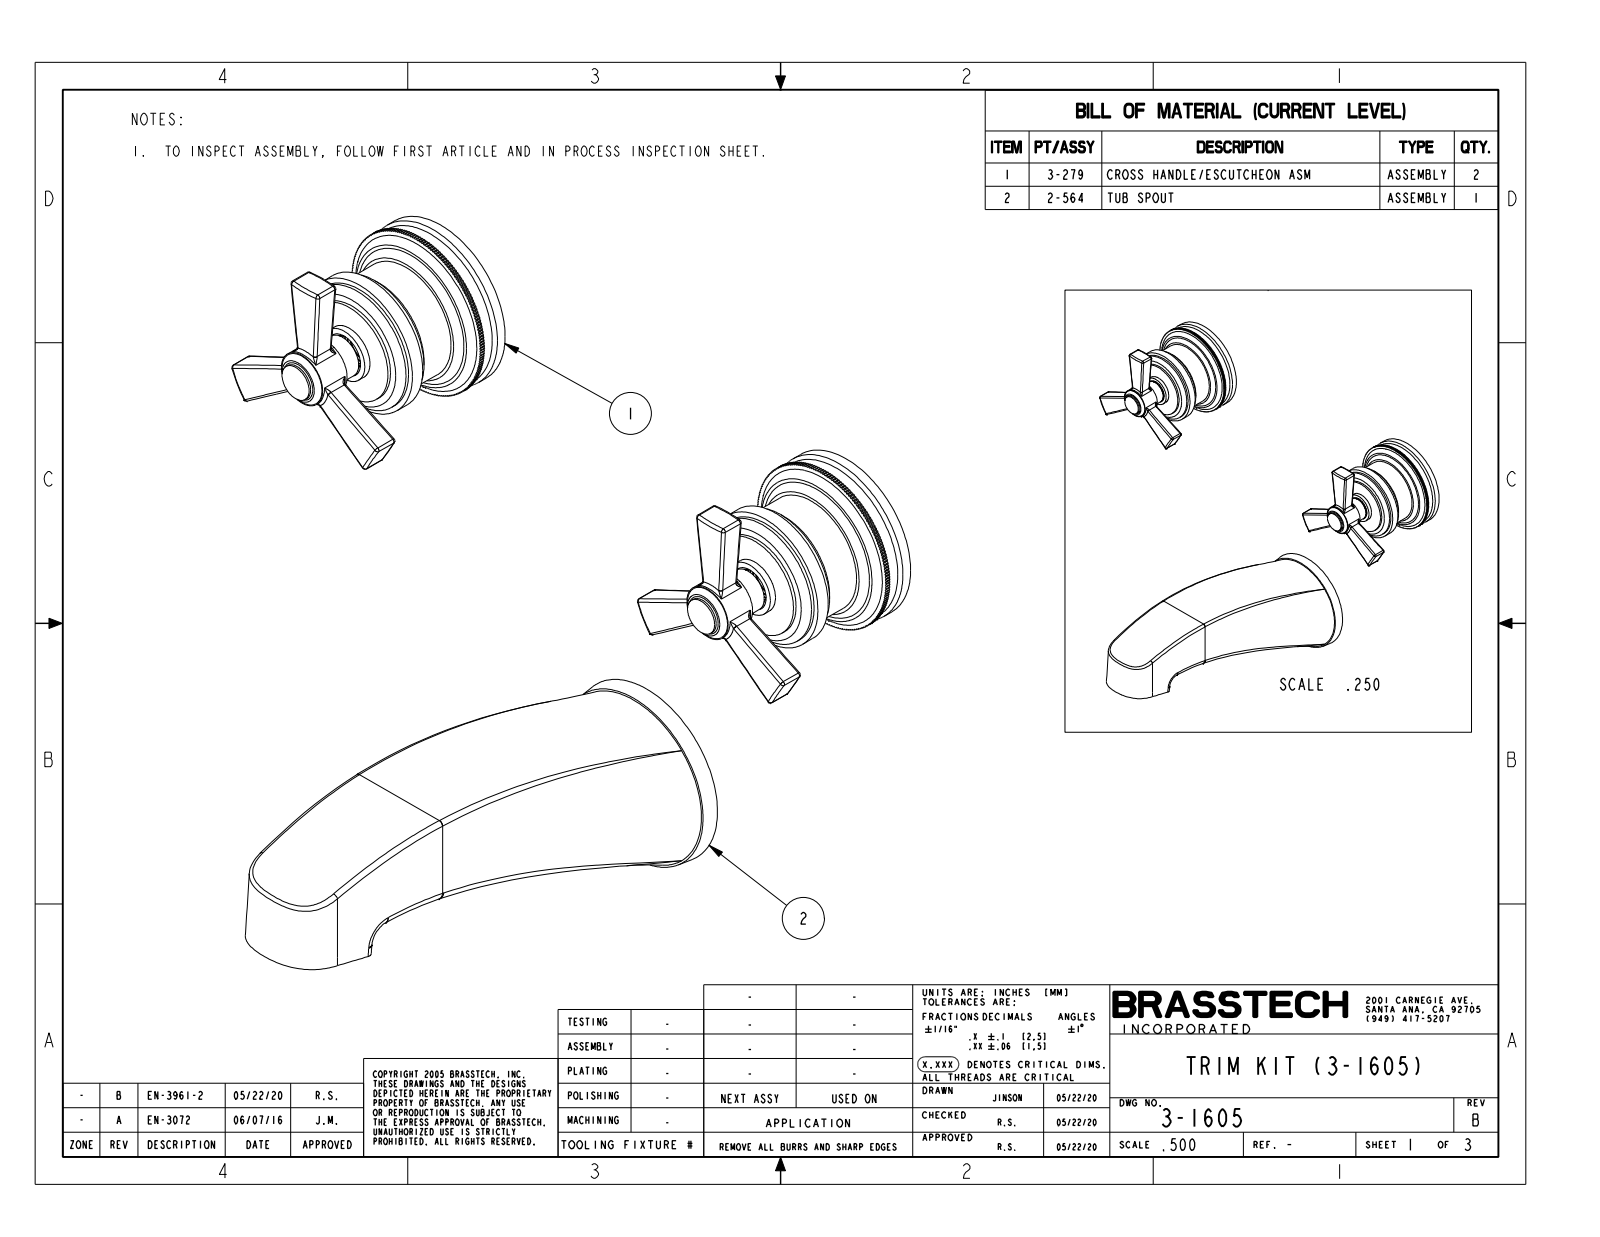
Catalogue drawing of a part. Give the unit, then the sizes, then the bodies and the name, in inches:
Units: inches
Overall size (bounding box): 10.714 × 8.875 × 7.429
Round bosses / shafts (diameter × count): ⌀2.5 ×2, ⌀2.4 ×2, ⌀2.05 ×2, ⌀1.9 ×2, ⌀1.75 ×2, ⌀1.5 ×2, ⌀0.8 ×2, ⌀0.625 ×2
Partial cylindrical surfaces — rounded edges, fillets, slot ends (radius × count): R0.04 ×12, R0.1 ×12
Main face-to-face distances: 0.062, 1.837, 1.775, 0.2, 0.1, 1.3, 0.15, 0.4, 1.375, 0.9
Volume: 36.29 in³ · Surface area: 117.7 in²
Bodies: 3 solids, 1419 faces (772 planar, 432 cylindrical, 215 other)
Part name (STEP PRODUCT): 3-1605_SW0001
STEP written by: CREO PARAMETRIC BY PTC INC, 2018400 (AUTOMOTIVE_DESIGN)
